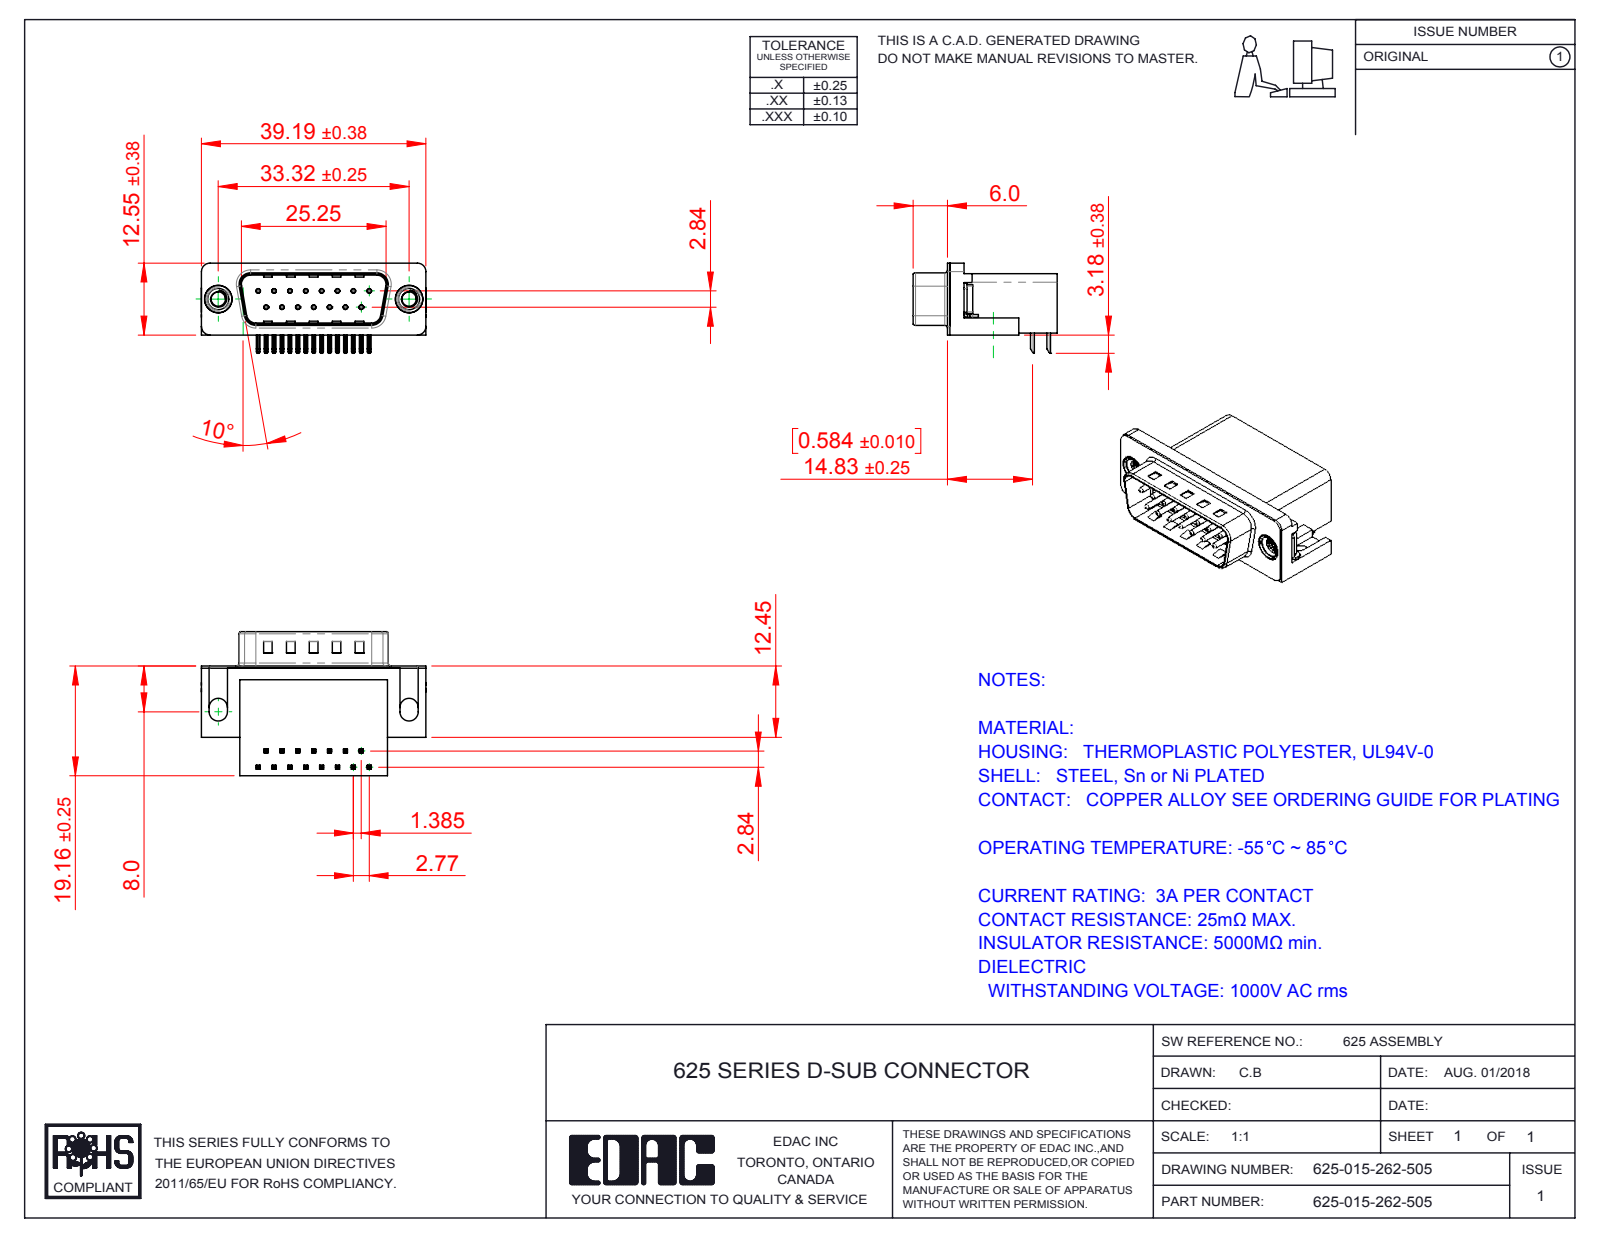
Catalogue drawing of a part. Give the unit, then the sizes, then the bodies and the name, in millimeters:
Units: millimetres
Overall size (bounding box): 39.22 × 25.16 × 15.73
Round holes (diameter × count): ⌀0.35 ×15, ⌀0.8 ×15, ⌀2.5 ×2, ⌀4 ×2, ⌀4.8 ×2, ⌀5 ×2
Round bosses / shafts (diameter × count): ⌀0.75 ×15, ⌀4.9 ×2, ⌀4.75 ×2, ⌀3.9 ×2
Partial cylindrical surfaces — rounded edges, fillets, slot ends (radius × count): R0.25 ×68, R0.12 ×30, R1 ×16, R0.5 ×9, R1.6 ×8, R1.5 ×6, R0.9 ×4, R2 ×4
Main face-to-face distances: 0.4, 10.35, 18.76, 2.1, 10.46, 19.16, 1.7, 10.86, 8.76, 16.26
Hole centre spacings: 3.16, 2.77, 5.54, 8.31, 11.08, 5.03, 5.04, 7.48
Volume: 6 210 mm³ · Surface area: 6 294 mm²
Bodies: 21 solids, 1477 faces (895 planar, 447 cylindrical, 135 other)
Part name (STEP PRODUCT): 625-015-262-505; 625 M3 Threaded Rivet; 625 Contact Bottom; 625 Shell_15 Socket (+3 more)
STEP written by: SolidWorks 2016 (CONFIG_CONTROL_DESIGN)
